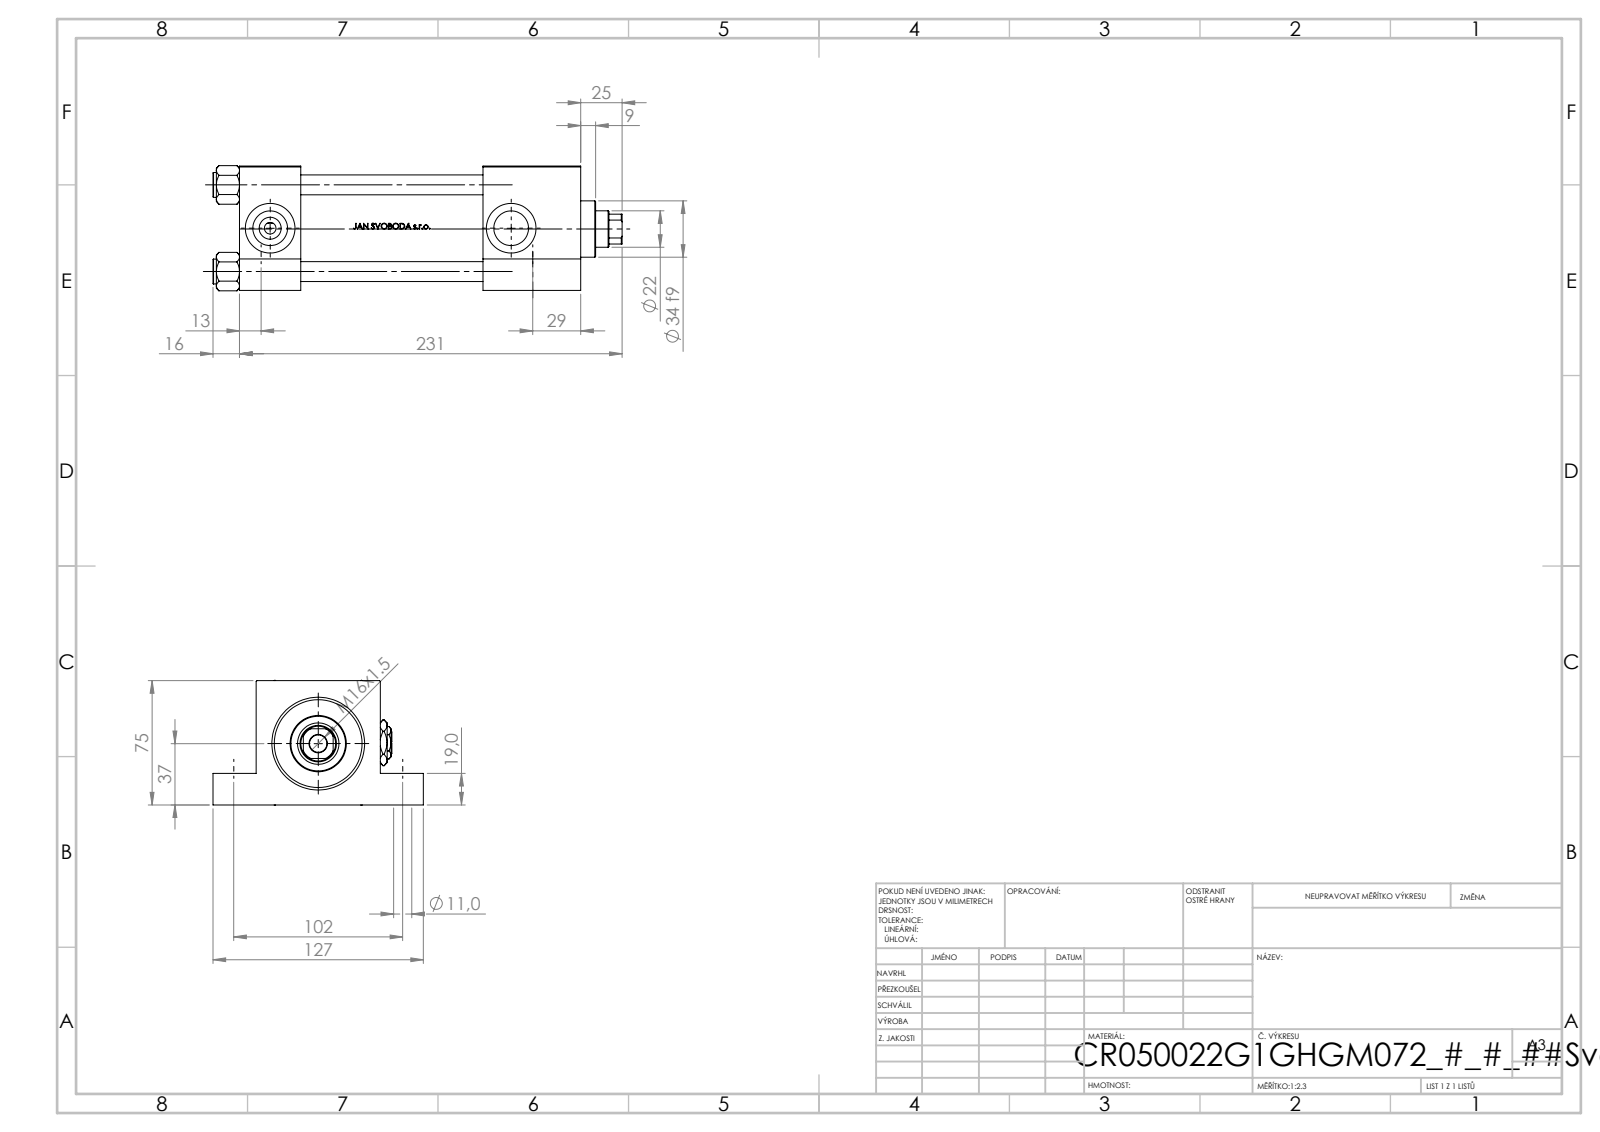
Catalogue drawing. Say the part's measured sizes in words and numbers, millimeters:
The part is named "V215CR_G_TYCINKA; V215CR_G_Body; Zatka_pro_OIL_PORT; NUT_M5_G (+2 more)". Its 3-D file was written by "SolidWorks 2019 (CONFIG_CONTROL_DESIGN)". It is 12 solids with 1134 faces: 454 planar, 128 cylindrical and 552 other. Overall it measures 247 by 127 by 75.54 millimeters. Its volume is 821 669 cubic millimeters and its surface area 190 056 square millimeters. Round holes: 4 of diameter 11, 4 of diameter 12, 2 of diameter 7, 2 of diameter 20.96, 2 of diameter 30, 1 of diameter 10.5, 1 of diameter 22, 1 of diameter 25, 1 of diameter 41, 1 of diameter 50, 1 of diameter 53. Round bosses or shafts: 4 of diameter 15, 1 of diameter 56, 1 of diameter 34. Partial cylindrical surfaces (rounded edges, fillets, slot ends): 1 of radius 10.5. The main face-to-face distances are 75, 37, 206, 169, 19, 56, 147, 110, 59, 26. The hole center spacings are 52.3, 36.63, 37.34, 73.96, 102, 164, 193.13, 145.5.
